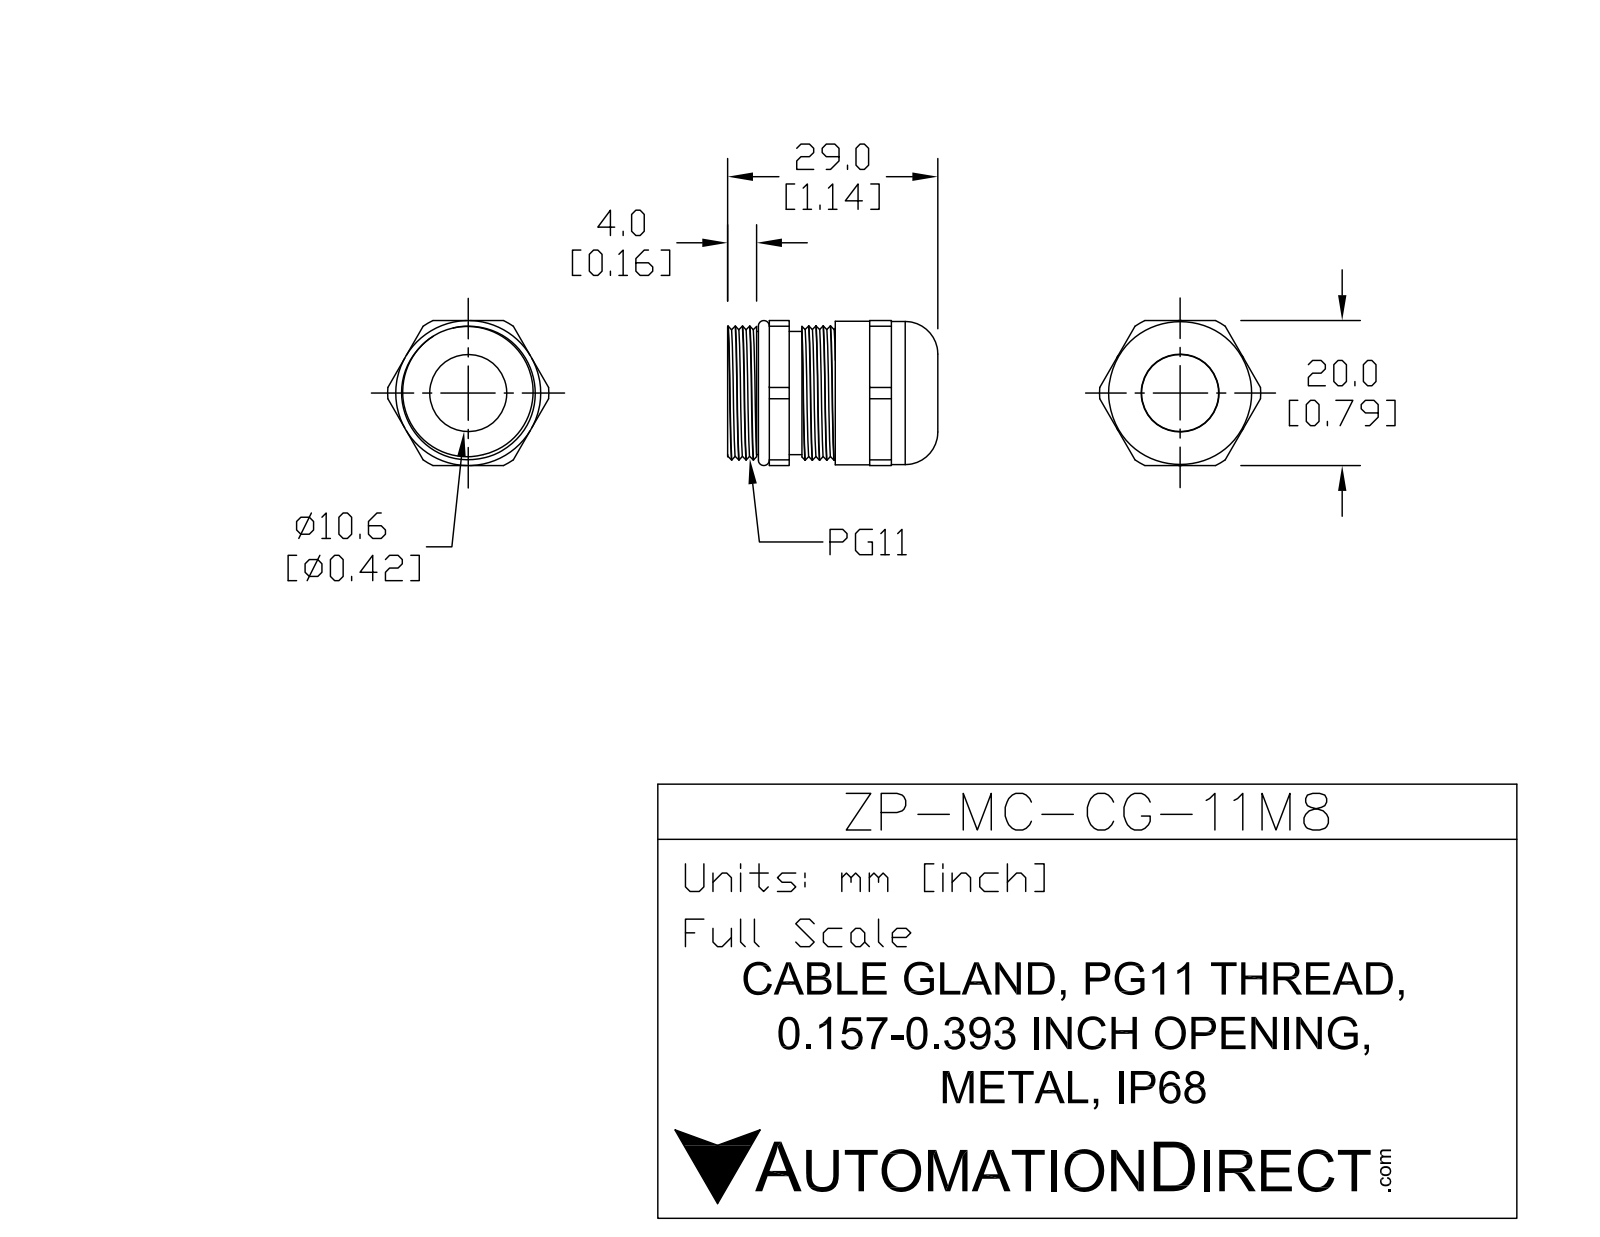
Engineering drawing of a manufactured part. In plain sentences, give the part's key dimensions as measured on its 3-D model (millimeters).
The part is named "ZP-MC-CG-11M8". Its 3-D file was written by "SolidWorks 2011 (AUTOMOTIVE_DESIGN)". It is 2 solids with 56 faces: 24 planar, 23 cylindrical and 9 other. Overall it measures 29.15 by 22.25 by 20 millimeters. Its volume is 5 677 cubic millimeters and its surface area 3 991 square millimeters. Round holes: 1 of diameter 10.65, 1 of diameter 18.97. Round bosses or shafts: 1 of diameter 19.8, 1 of diameter 19.75, 1 of diameter 18.5, 1 of diameter 18.45, 1 of diameter 17. Partial cylindrical surfaces (rounded edges, fillets, slot ends): 1 of radius 9.38, 1 of radius 11.12. The main face-to-face distances are 20, 8.5, 5.75, 2.75, 1.75, 4.5, 4.75, 22.75, 17, 14.25.
